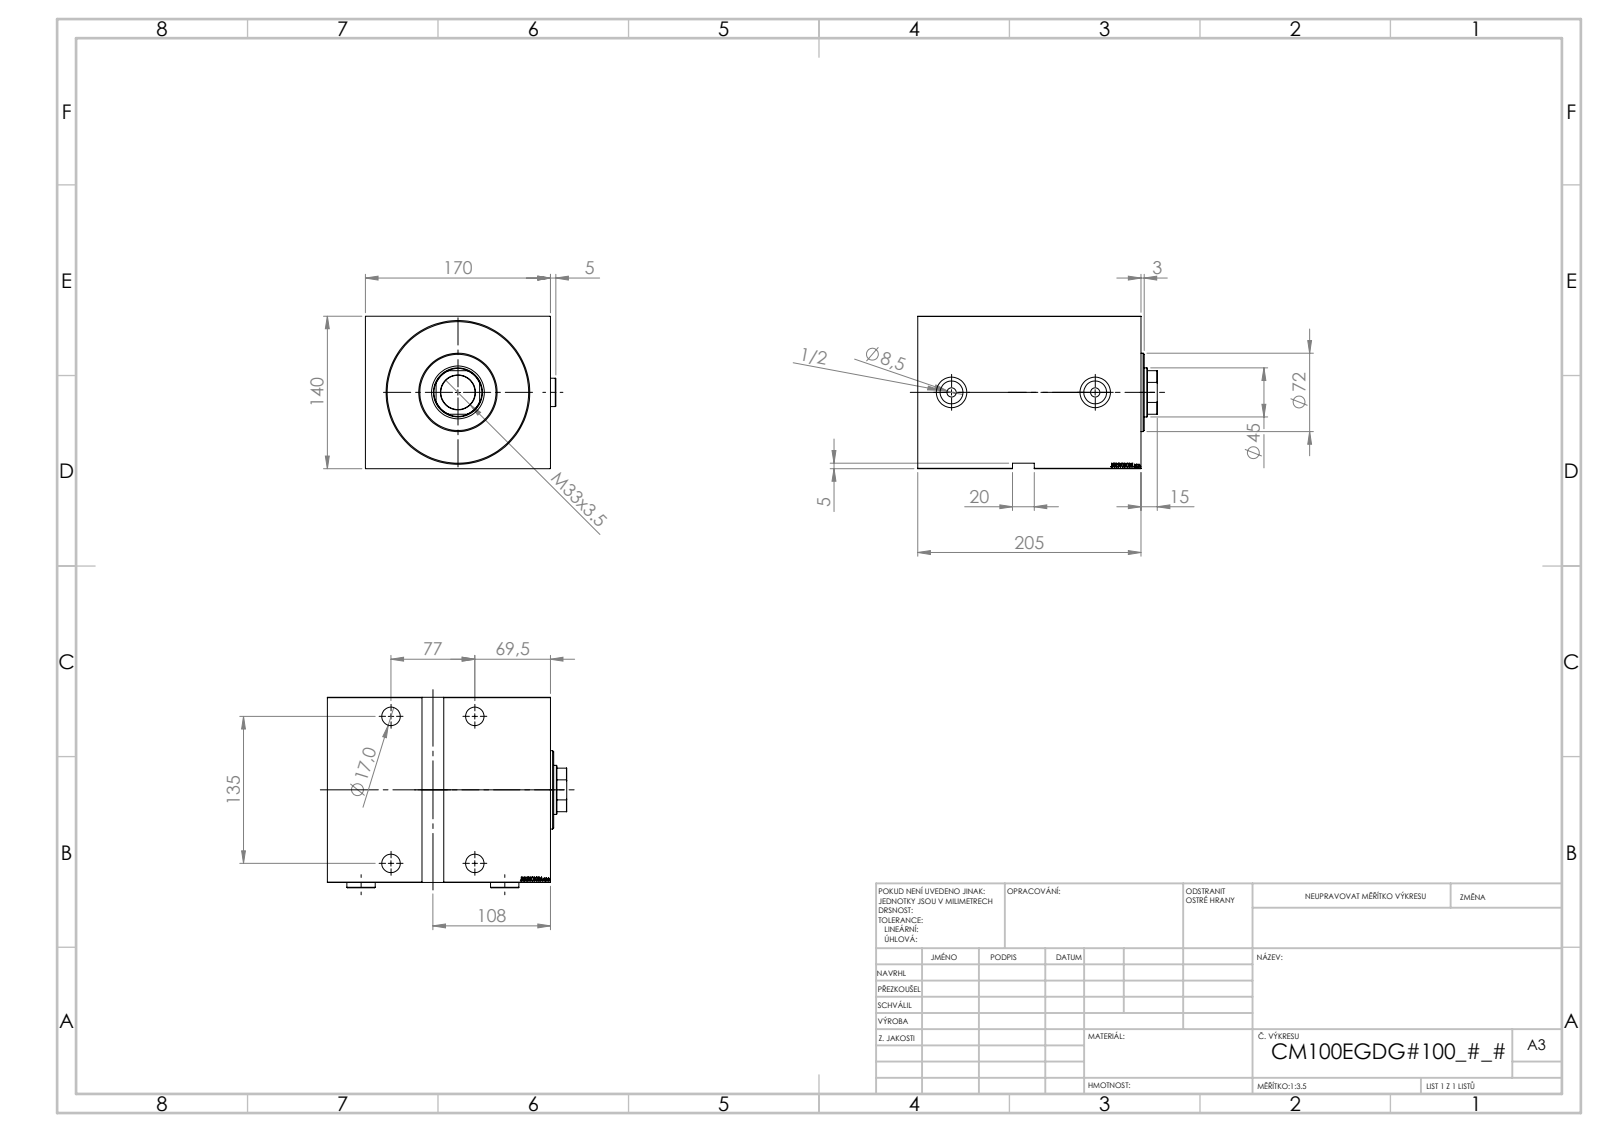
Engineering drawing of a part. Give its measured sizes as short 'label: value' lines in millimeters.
name: Zatka_OIL_PORT; V450CM_E_VCP; V450CM_E_Body; V450CM_VC_B
written by: SolidWorks 2019 (CONFIG_CONTROL_DESIGN)
unit: mm
bodies: 5 solids, 912 faces (446 planar, 68 cylindrical, 398 other)
size: 220 × 174.9 × 140
volume: 4 069 000 mm³; area: 362 287 mm²
holes: 4× ⌀17, 4× ⌀25, 2× ⌀8.5, 2× ⌀20.96, 2× ⌀28, 1× ⌀31.5, 1× ⌀45, 1× ⌀48.5, 1× ⌀100, 1× ⌀130
bosses: 2× ⌀26, 1× ⌀102, 1× ⌀72
rounds: 1× R22
face distances: 140, 170, 205, 26, 179, 5, 200, 174, 90, 188.4
hole spacings: 77, 135, 155.42, 132
